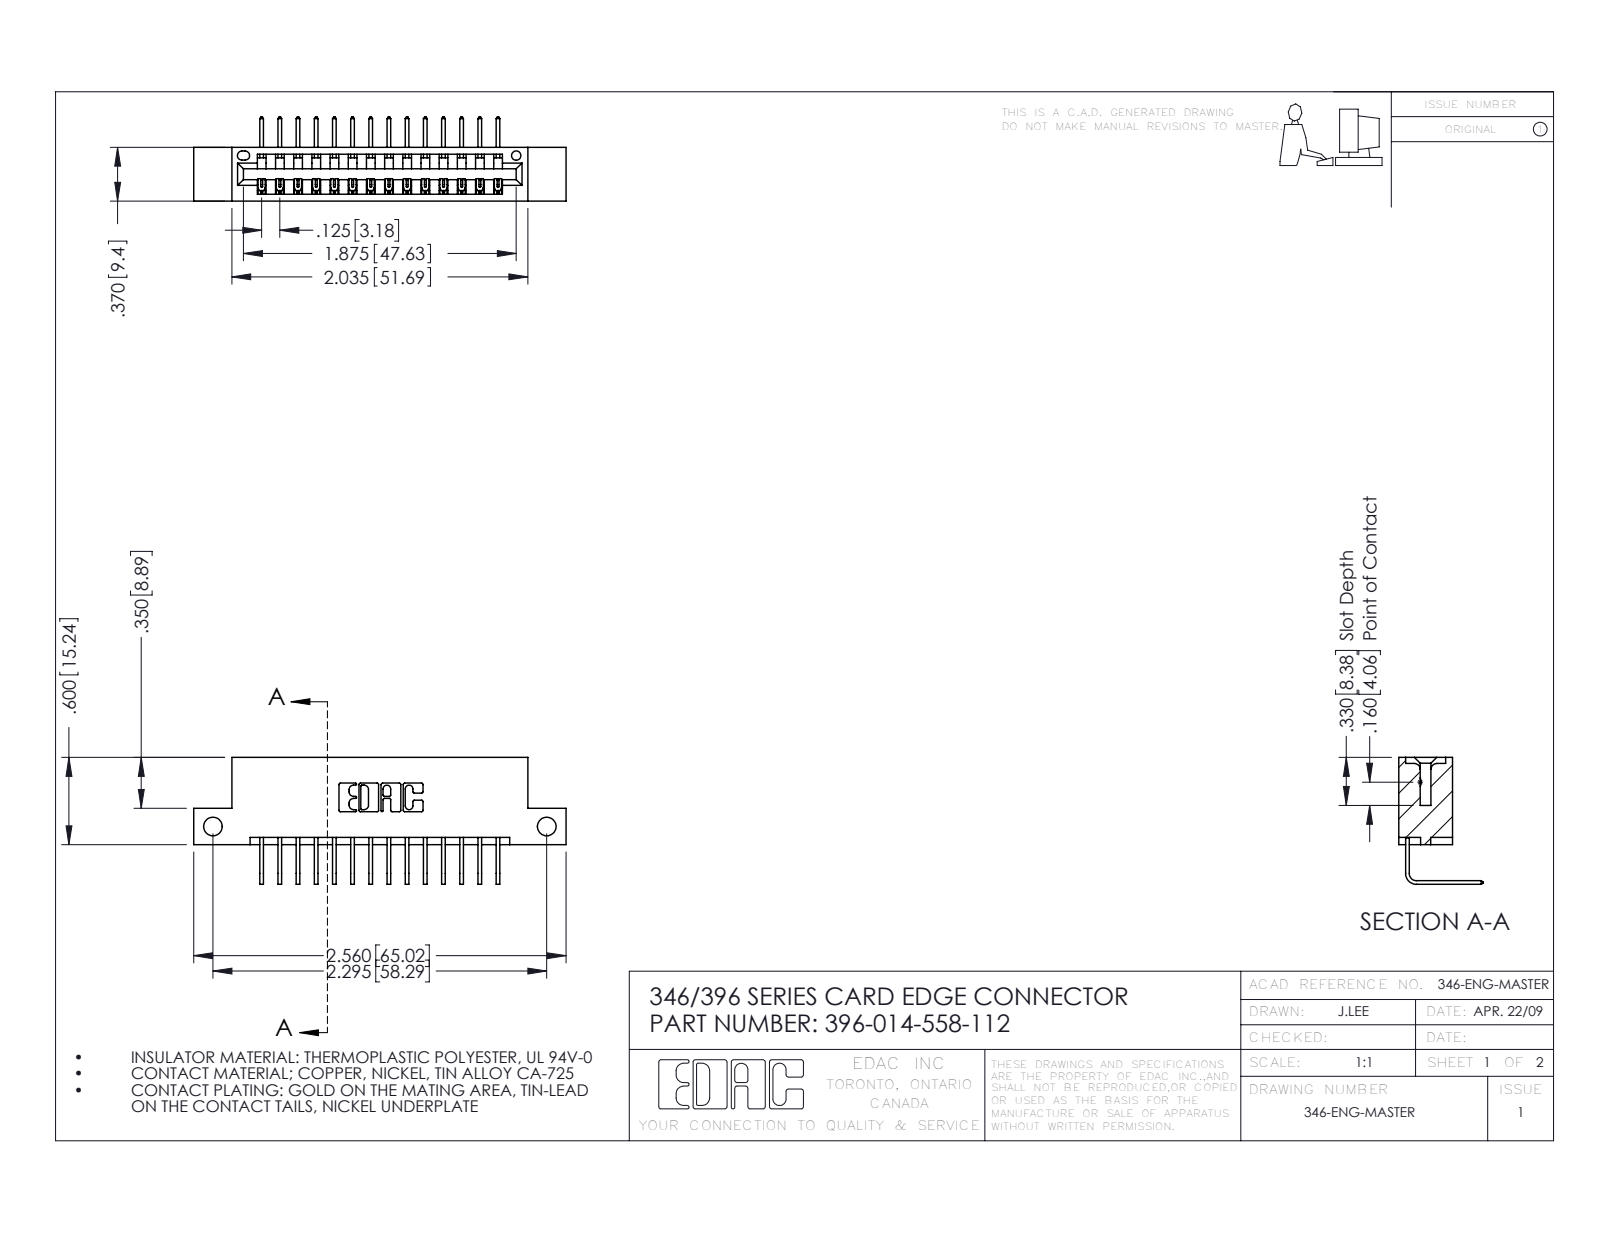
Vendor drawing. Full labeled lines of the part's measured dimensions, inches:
Part name (STEP PRODUCT): 345-292-001_558 Tail - 2; 396-014-558-112; 346 Part_Flush Mounting Lugs - Side Mount
STEP written by: SolidWorks 2016 (CONFIG_CONTROL_DESIGN)
Units: inches
Bodies: 15 solids, 962 faces (664 planar, 298 cylindrical, 0 other)
Overall size (bounding box): 2.56 × 0.873 × 0.58
Volume: 0.366 in³ · Surface area: 11.34 in²
Round holes (diameter × count): ⌀0.128 ×2, ⌀0.064 ×1
Partial cylindrical surfaces — rounded edges, fillets, slot ends (radius × count): R0.006 ×28, R0.01 ×22, R0.007 ×6, R0.031 ×6, R0.026 ×3, R0.031 ×2, R0.04 ×2, R0.014 ×1
Main face-to-face distances: 0.322, 0.25, 0.048, 0.37, 0.298, 0.025, 0.072, 0.148, 0.222, 0.1
Hole centre spacings: 2.295
